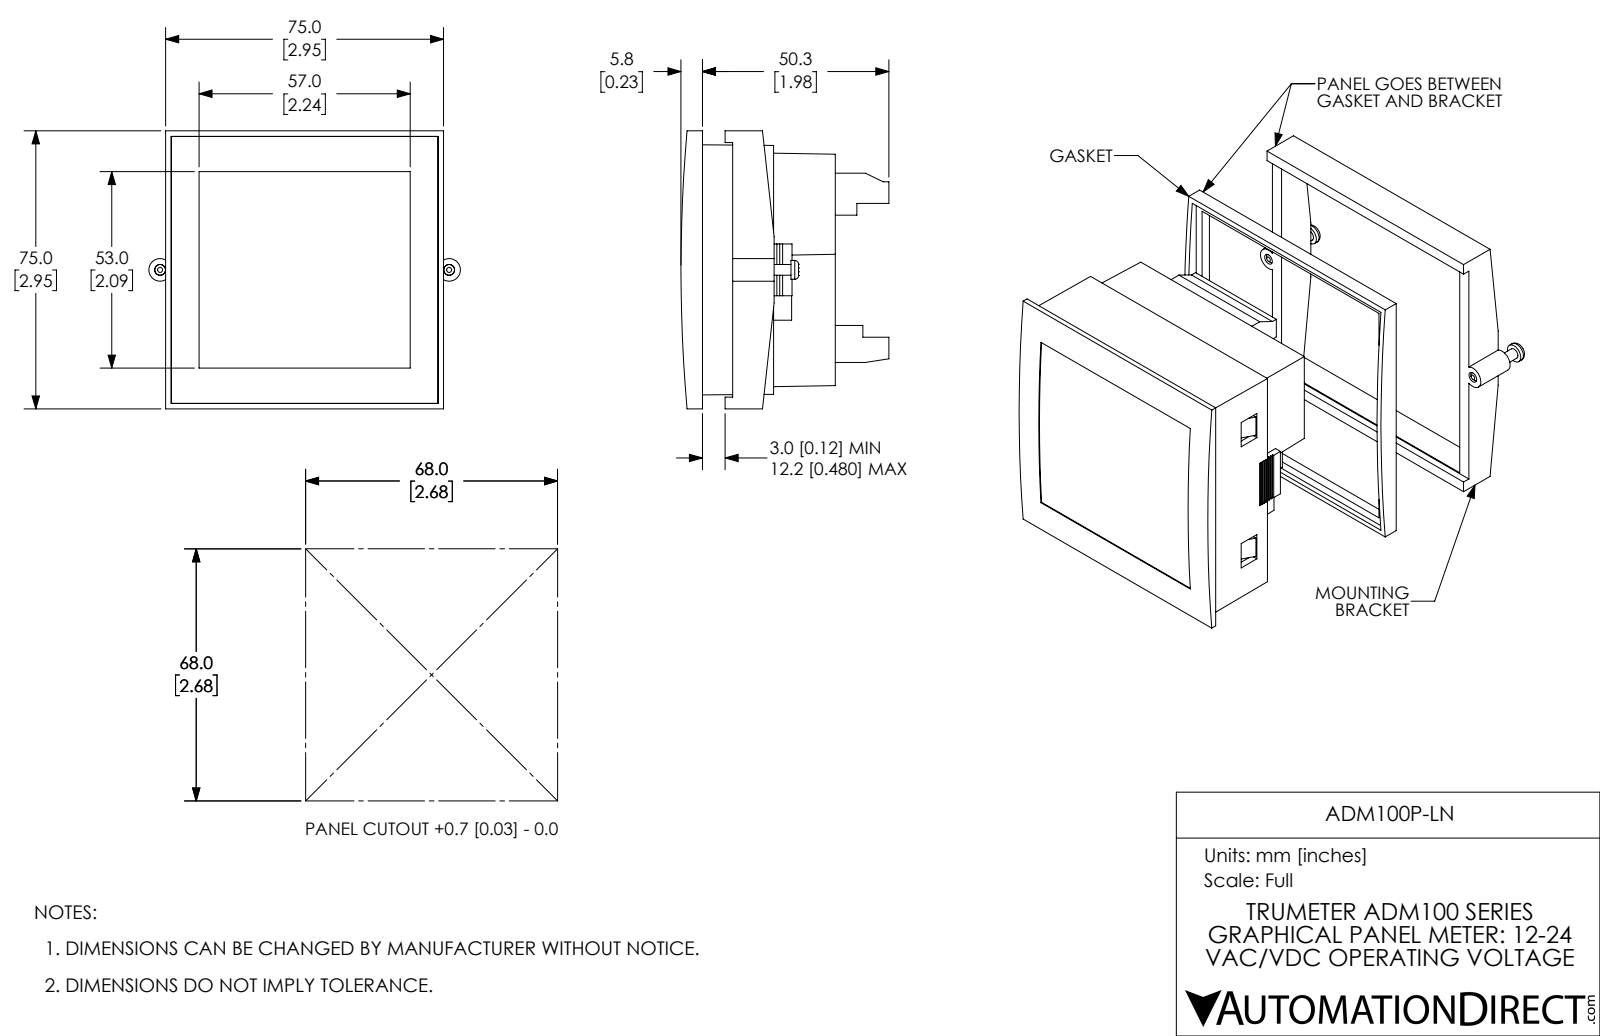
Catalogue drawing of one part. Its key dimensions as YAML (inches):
part_name: "ADM100P-LN"
step_written_by: "SolidWorks 2021 (CONFIG_CONTROL_DESIGN)"
units: inches
bodies: {solids: 23, faces: 419, planar: 335, cylindrical: 76, other: 8}
overall_size: [3.311, 2.953, 2.209]
volume: 9.565
surface_area: 90.64
round_holes:
  - {diameter: 0.151, count: 13}
  - {diameter: 0.115, count: 2}
round_bosses_or_shafts:
  - {diameter: 0.148, count: 13}
  - {diameter: 0.2, count: 2}
  - {diameter: 0.114, count: 2}
partial_cylinders:
  - {radius: 0.12, count: 2}
  - {radius: 17.037, count: 2}
face_to_face_distances: [0.075, 0.305, 0.236, 2.717, 2.657, 0.089, 0.148, 2.805, 2.583, 1.142]
hole_center_spacings: [1.653, 0.2, 1.677, 0.4, 1.724, 0.6, 1.792, 0.8]
